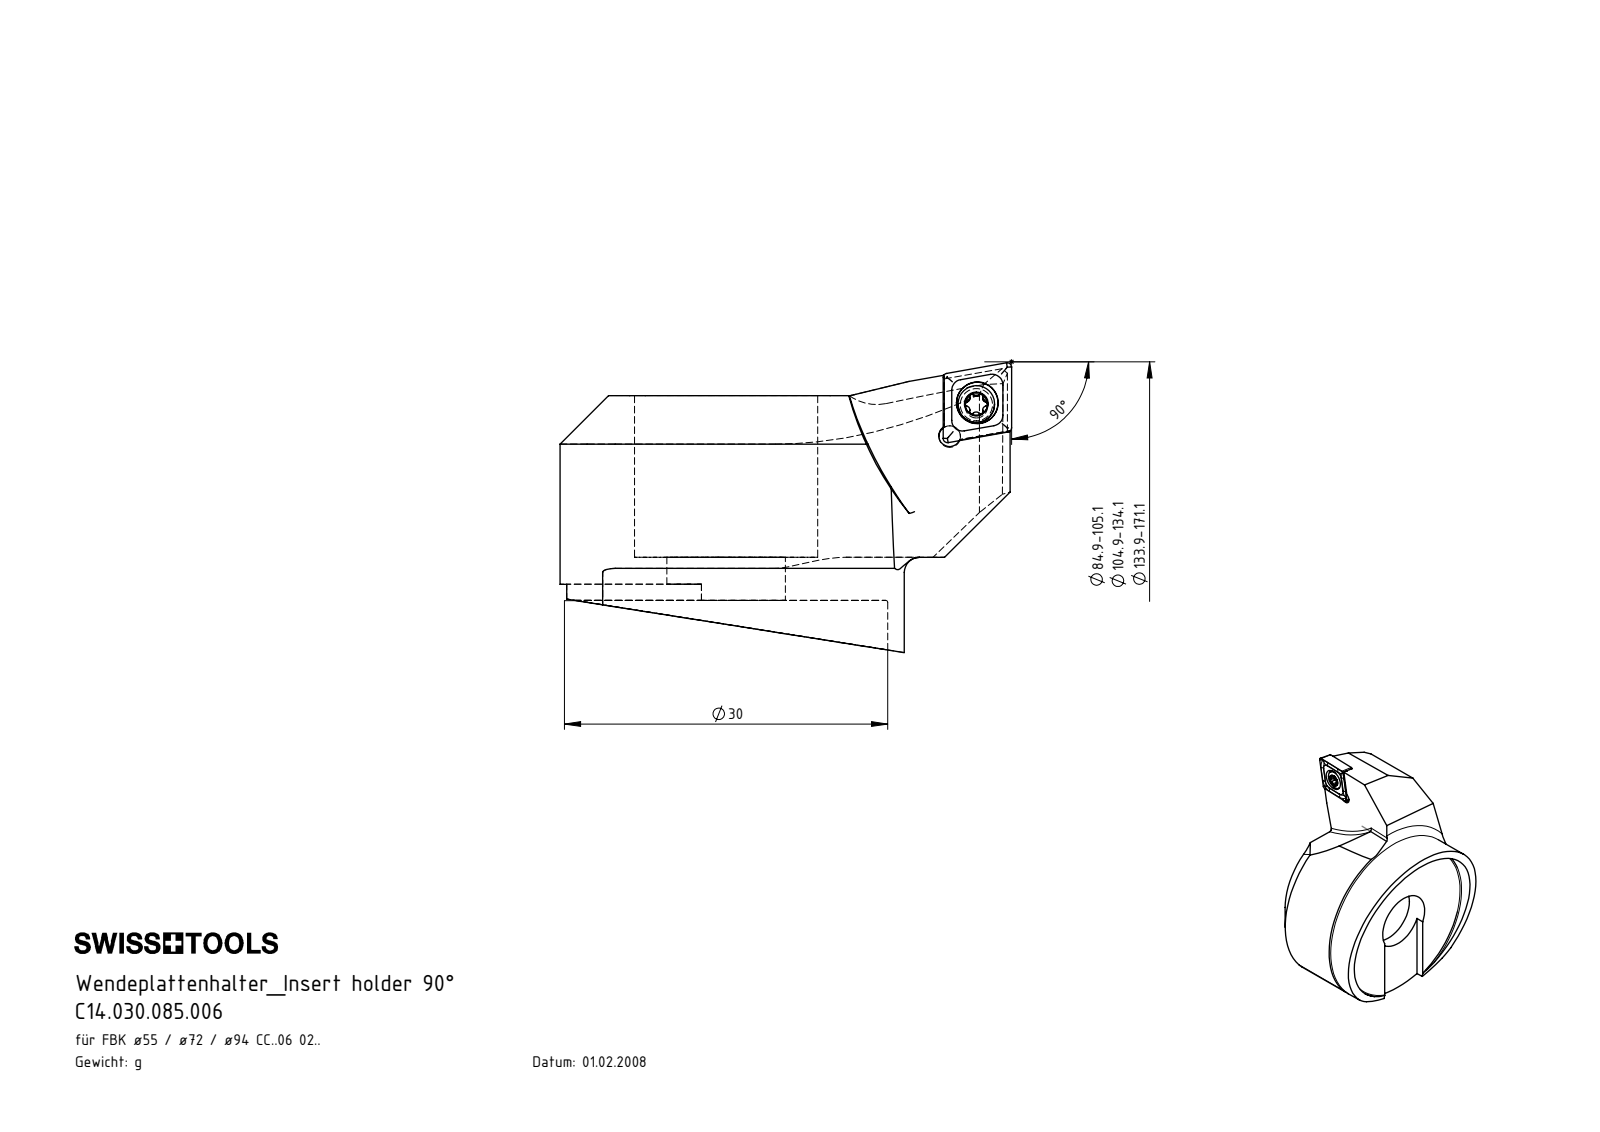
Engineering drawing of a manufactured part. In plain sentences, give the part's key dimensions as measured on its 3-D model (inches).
The part is named "WCA-ER2.001.006_A; CCMT060204; C14.030.085.006; F55-WCA.001.022_D_fertigbearbeitet". Its 3-D file was written by "SolidWorks 2017 (CONFIG_CONTROL_DESIGN)". It is 5 solids with 161 faces: 50 planar, 51 cylindrical and 60 other. Overall it measures 1.65 by 1.307 by 1.059 inches. Its volume is 0.836 cubic inches and its surface area 9.275 square inches. Round holes: 1 of diameter 0.079, 1 of diameter 0.081, 1 of diameter 0.11, 1 of diameter 0.152, 1 of diameter 0.433, 1 of diameter 0.669, 1 of diameter 1.181. Round bosses or shafts: 1 of diameter 0.134, 1 of diameter 0.098. Partial cylindrical surfaces (rounded edges, fillets, slot ends): 6 of radius 0.008, 5 of radius 0.014, 2 of radius 0.02, 2 of radius 0.394, 1 of radius 0.014, 1 of radius 0.197, 1 of radius 0.652, 1 of radius 0.654. The main face-to-face distances are 0.748, 0.039, 0.709, 0.591, 0.551, 0.157, 0.059, 0.689, 0.65, 0.098. The hole center spacings are 0.152, 0.158.
